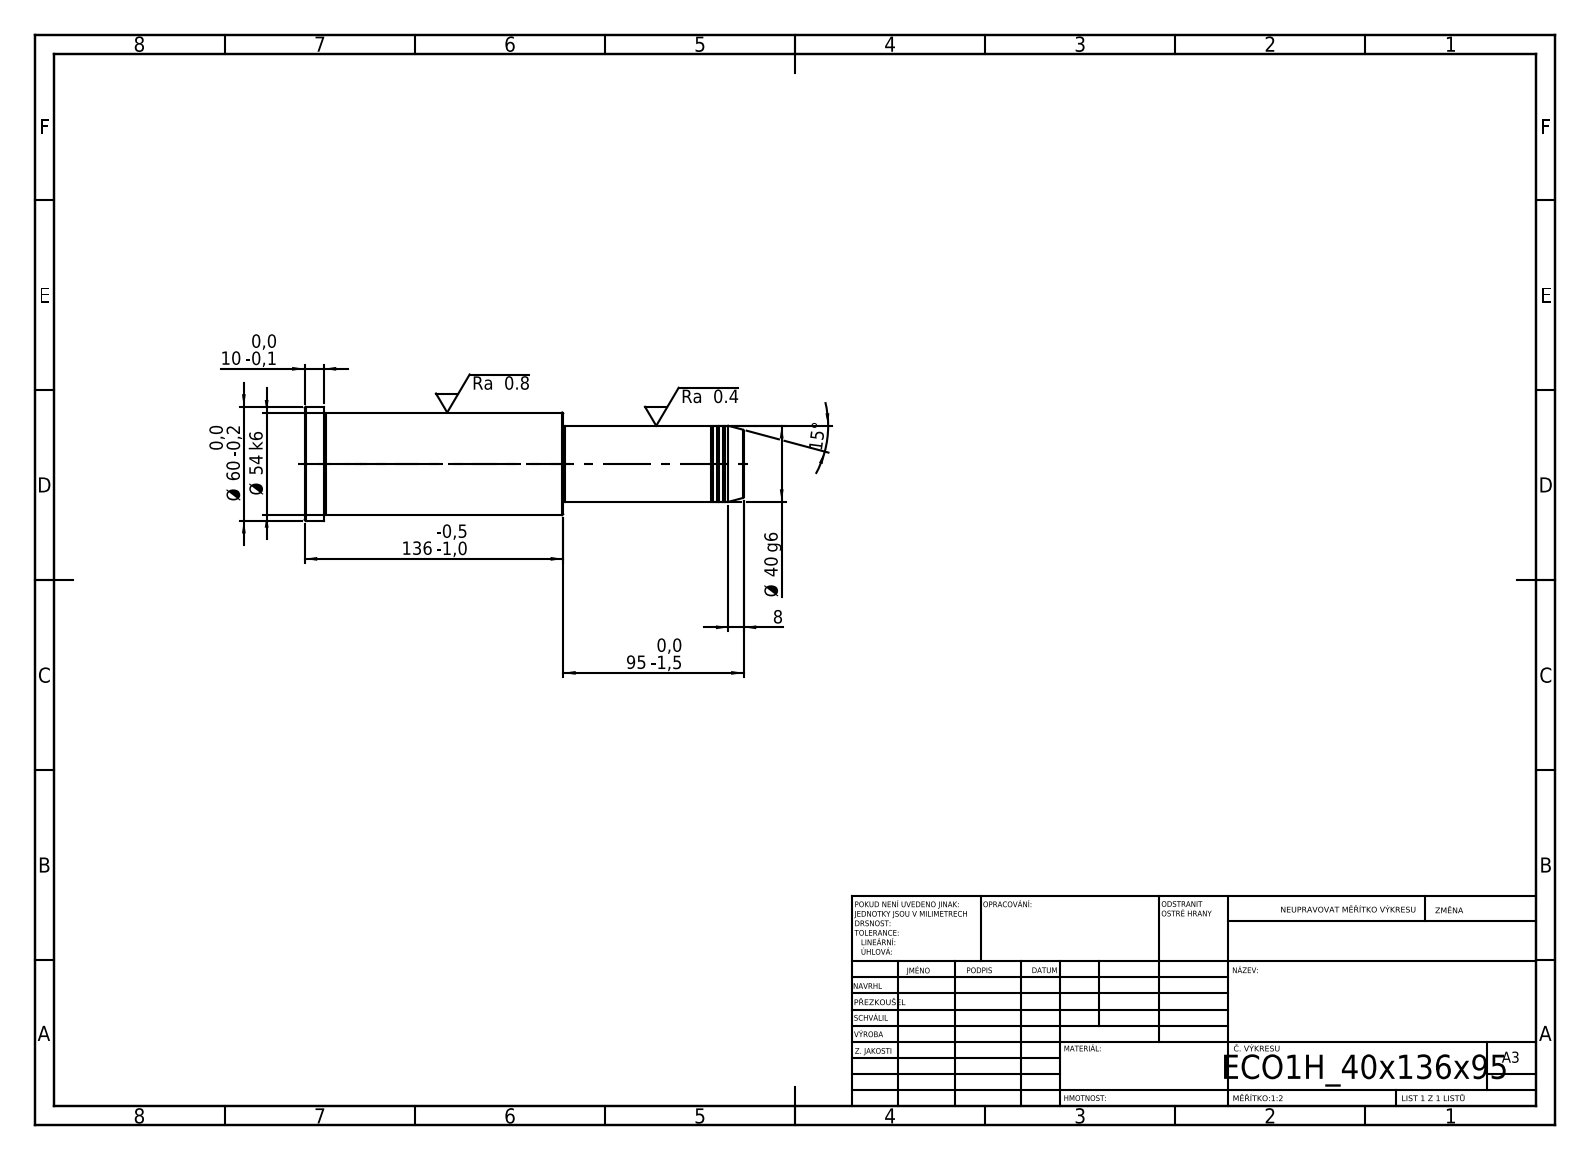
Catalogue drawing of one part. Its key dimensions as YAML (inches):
step_written_by: "SolidWorks 2019 (CONFIG_CONTROL_DESIGN)"
units: inches
bodies: {solids: 1, faces: 43, planar: 5, cylindrical: 14, other: 24}
overall_size: [9.094, 2.362, 2.362]
volume: 26.54
surface_area: 63.36
round_bosses_or_shafts:
  - {diameter: 2.362, count: 1}
  - {diameter: 2.126, count: 1}
  - {diameter: 1.575, count: 1}
  - {diameter: 1.535, count: 1}
face_to_face_distances: [5.354, 3.74, 9.094, 8.701, 4.961, 0.394, 3.701, 0.039, 5, 5.394]
